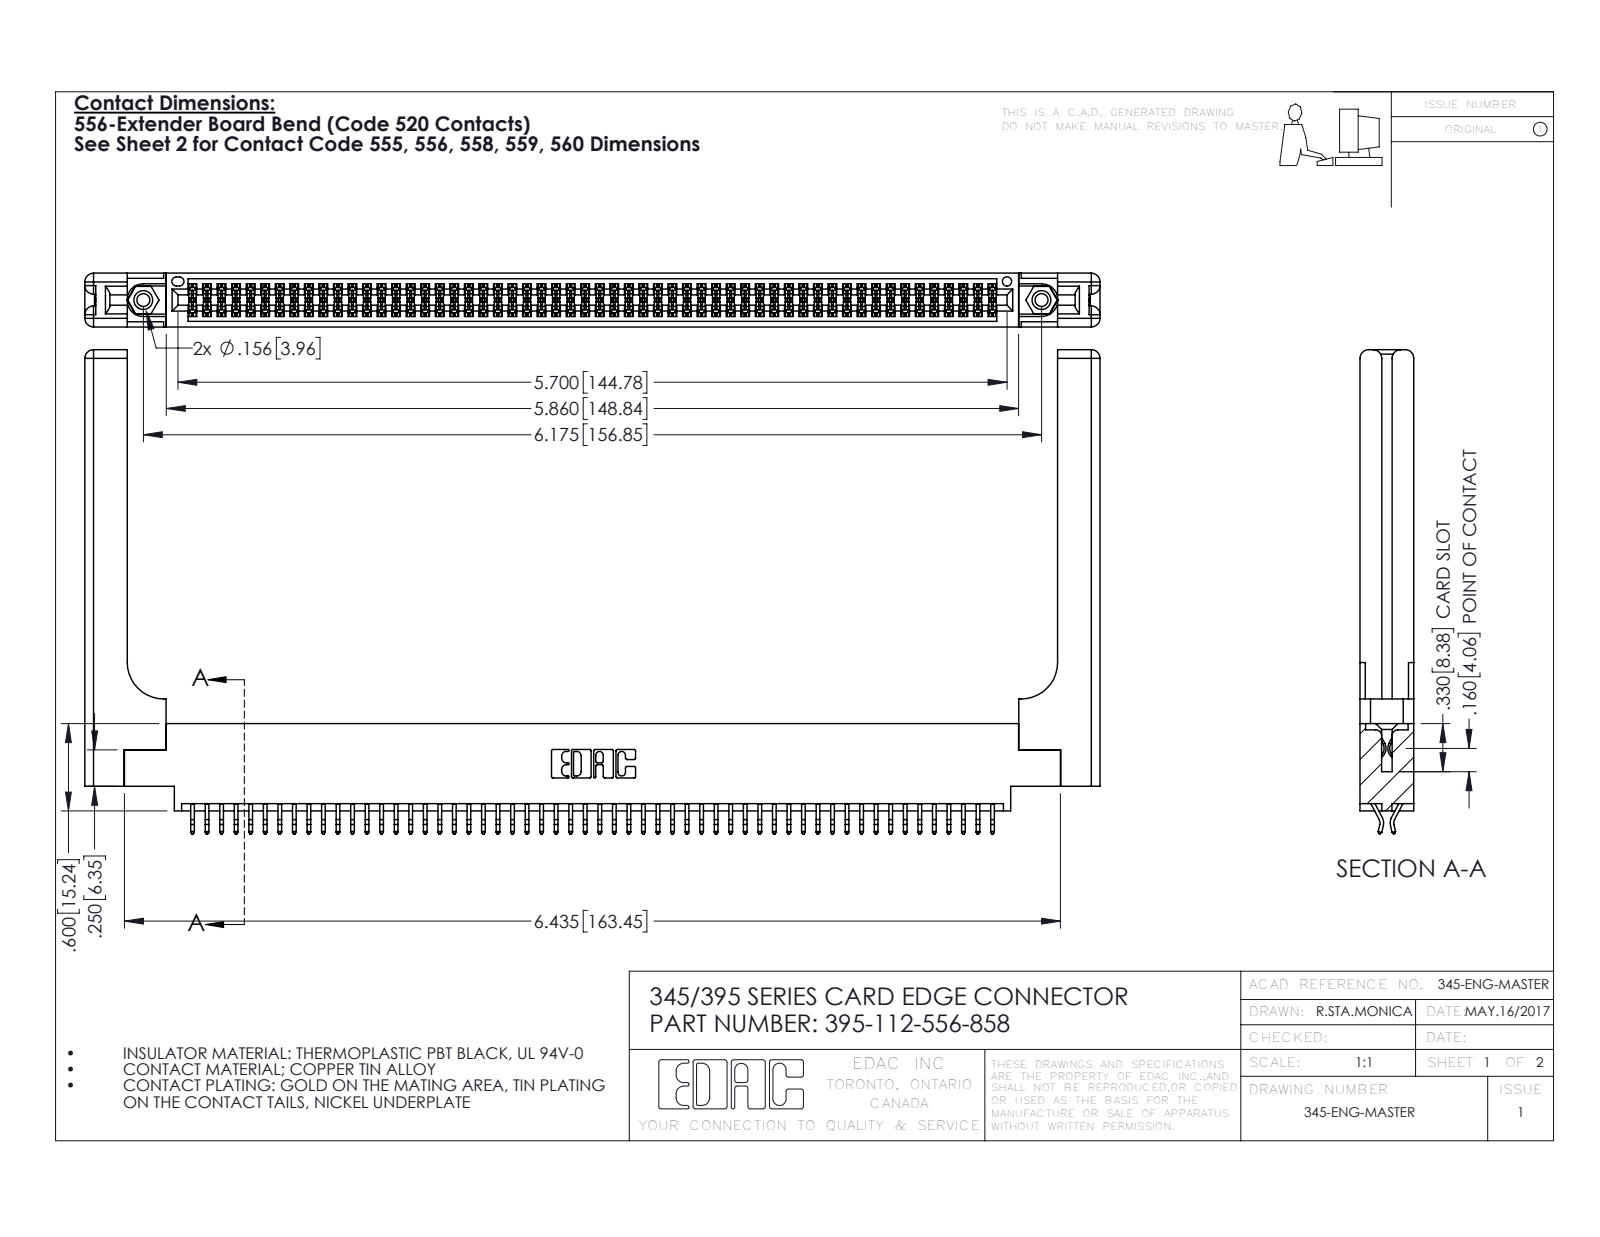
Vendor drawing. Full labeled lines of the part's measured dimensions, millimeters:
Part name (STEP PRODUCT): 345-250-001_345-250-001-102; 395-112-556-858; 345-292-001_556 Tail; 345-220-058_345-220-058 (+1 more)
STEP written by: SolidWorks 2016 (CONFIG_CONTROL_DESIGN)
Units: millimetres
Bodies: 117 solids, 6658 faces (4376 planar, 2222 cylindrical, 60 other)
Overall size (bounding box): 177.3 × 84.5 × 9.4
Volume: 25 710 mm³ · Surface area: 30 850 mm²
Round holes (diameter × count): ⌀2.3 ×2, ⌀3.2 ×2, ⌀4 ×2, ⌀1.6 ×1
Round bosses / shafts (diameter × count): ⌀3.9 ×2
Partial cylindrical surfaces — rounded edges, fillets, slot ends (radius × count): R0.2 ×168, R0.3 ×22, R1.5 ×16, R0.2 ×6, R0.8 ×6, R0.7 ×3, R0.3 ×2, R0.4 ×2
Main face-to-face distances: 1.8, 9.4, 7.6, 0.6, 2.5, 6.9, 5.1, 5.7, 4.4, 3.8
Hole centre spacings: 6.9, 150.9, 156.8
